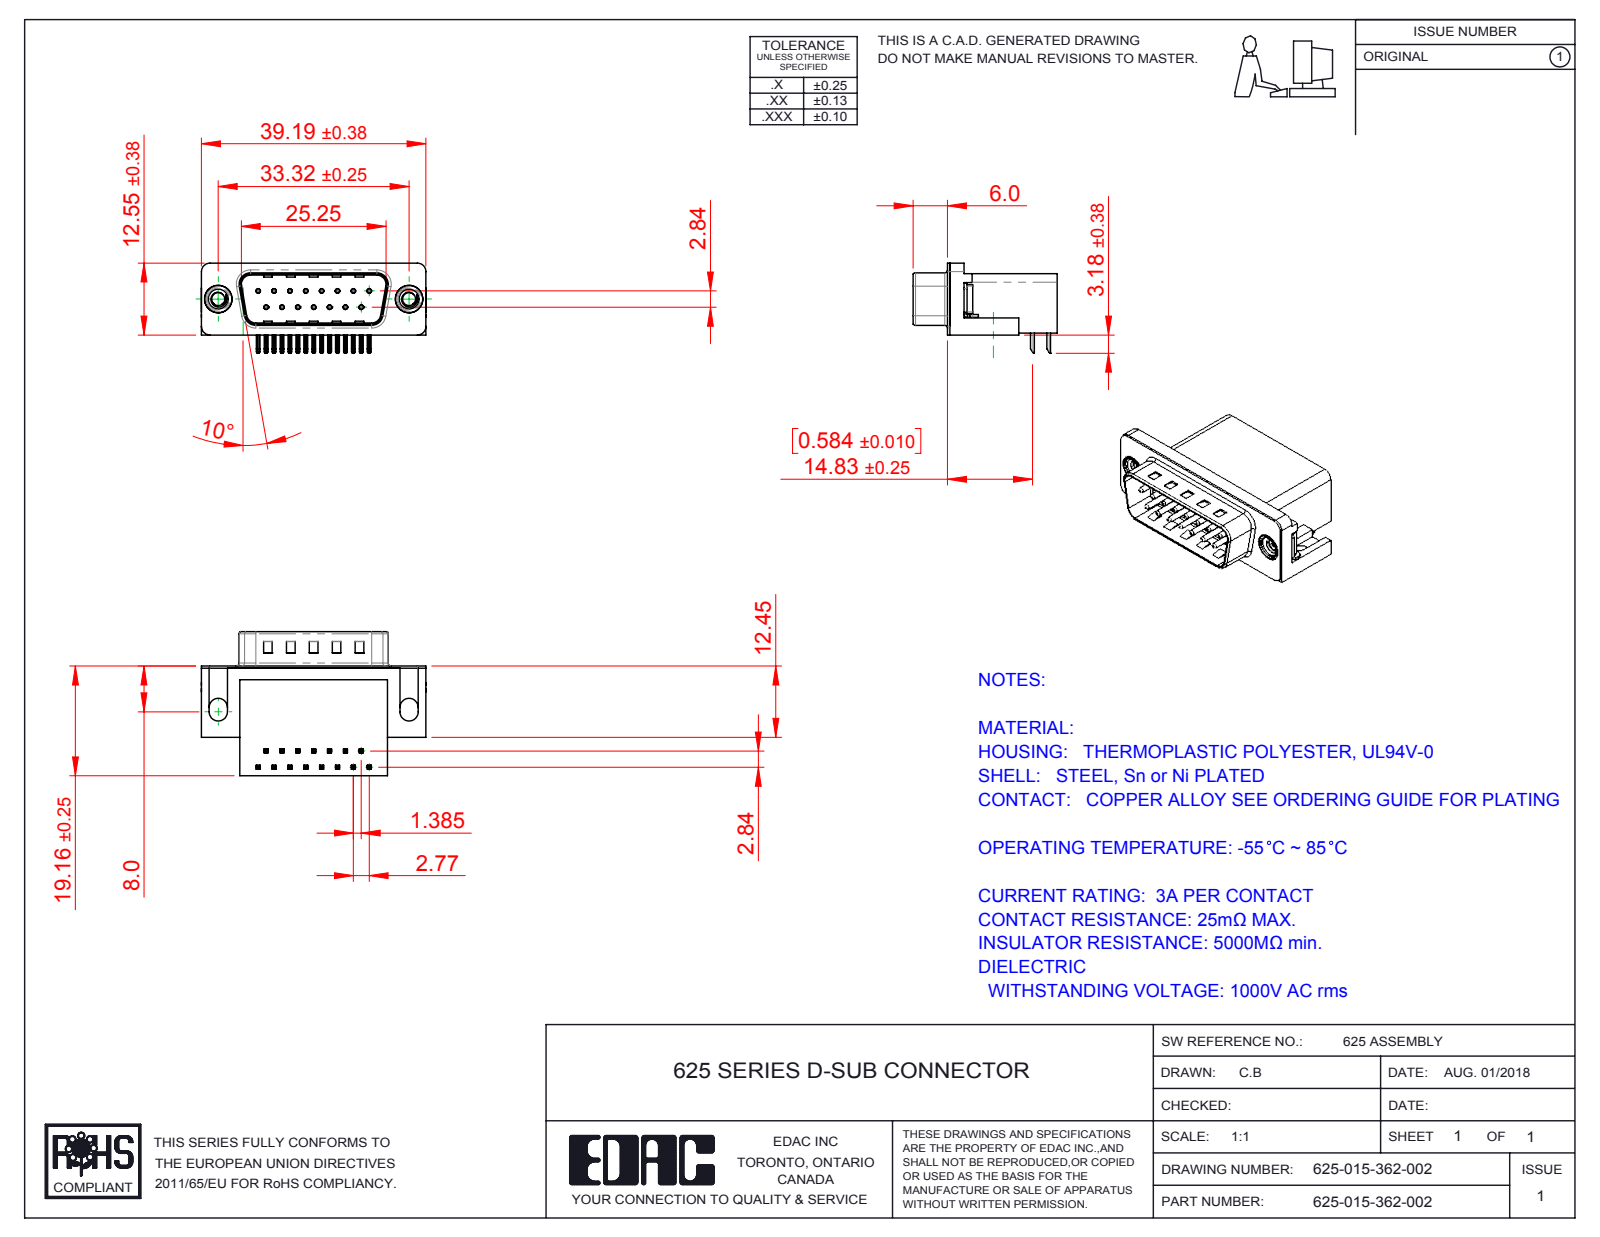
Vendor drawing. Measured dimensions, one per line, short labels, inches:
name: 625 4-40 Threaded Rivet; 625 Non Board Mount; 625 Housing_15 Socket; 625 Contact Bottom (+3 more)
written by: SolidWorks 2016 (CONFIG_CONTROL_DESIGN)
unit: in
bodies: 21 solids, 1477 faces (895 planar, 443 cylindrical, 139 other)
size: 1.544 × 0.991 × 0.619
volume: 0.379 in³; area: 9.751 in²
holes: 15× ⌀0.014, 15× ⌀0.031, 2× ⌀0.089, 2× ⌀0.157, 2× ⌀0.189, 2× ⌀0.197
bosses: 15× ⌀0.03, 2× ⌀0.193, 2× ⌀0.187, 2× ⌀0.154
rounds: 68× R0.01, 30× R0.005, 16× R0.039, 9× R0.02, 8× R0.063, 6× R0.059, 4× R0.035, 4× R0.079
face distances: 0.016, 0.407, 0.739, 0.083, 0.412, 0.754, 0.067, 0.428, 0.345, 0.64
hole spacings: 0.124, 0.109, 0.218, 0.327, 0.436, 0.198, 0.198, 0.294
